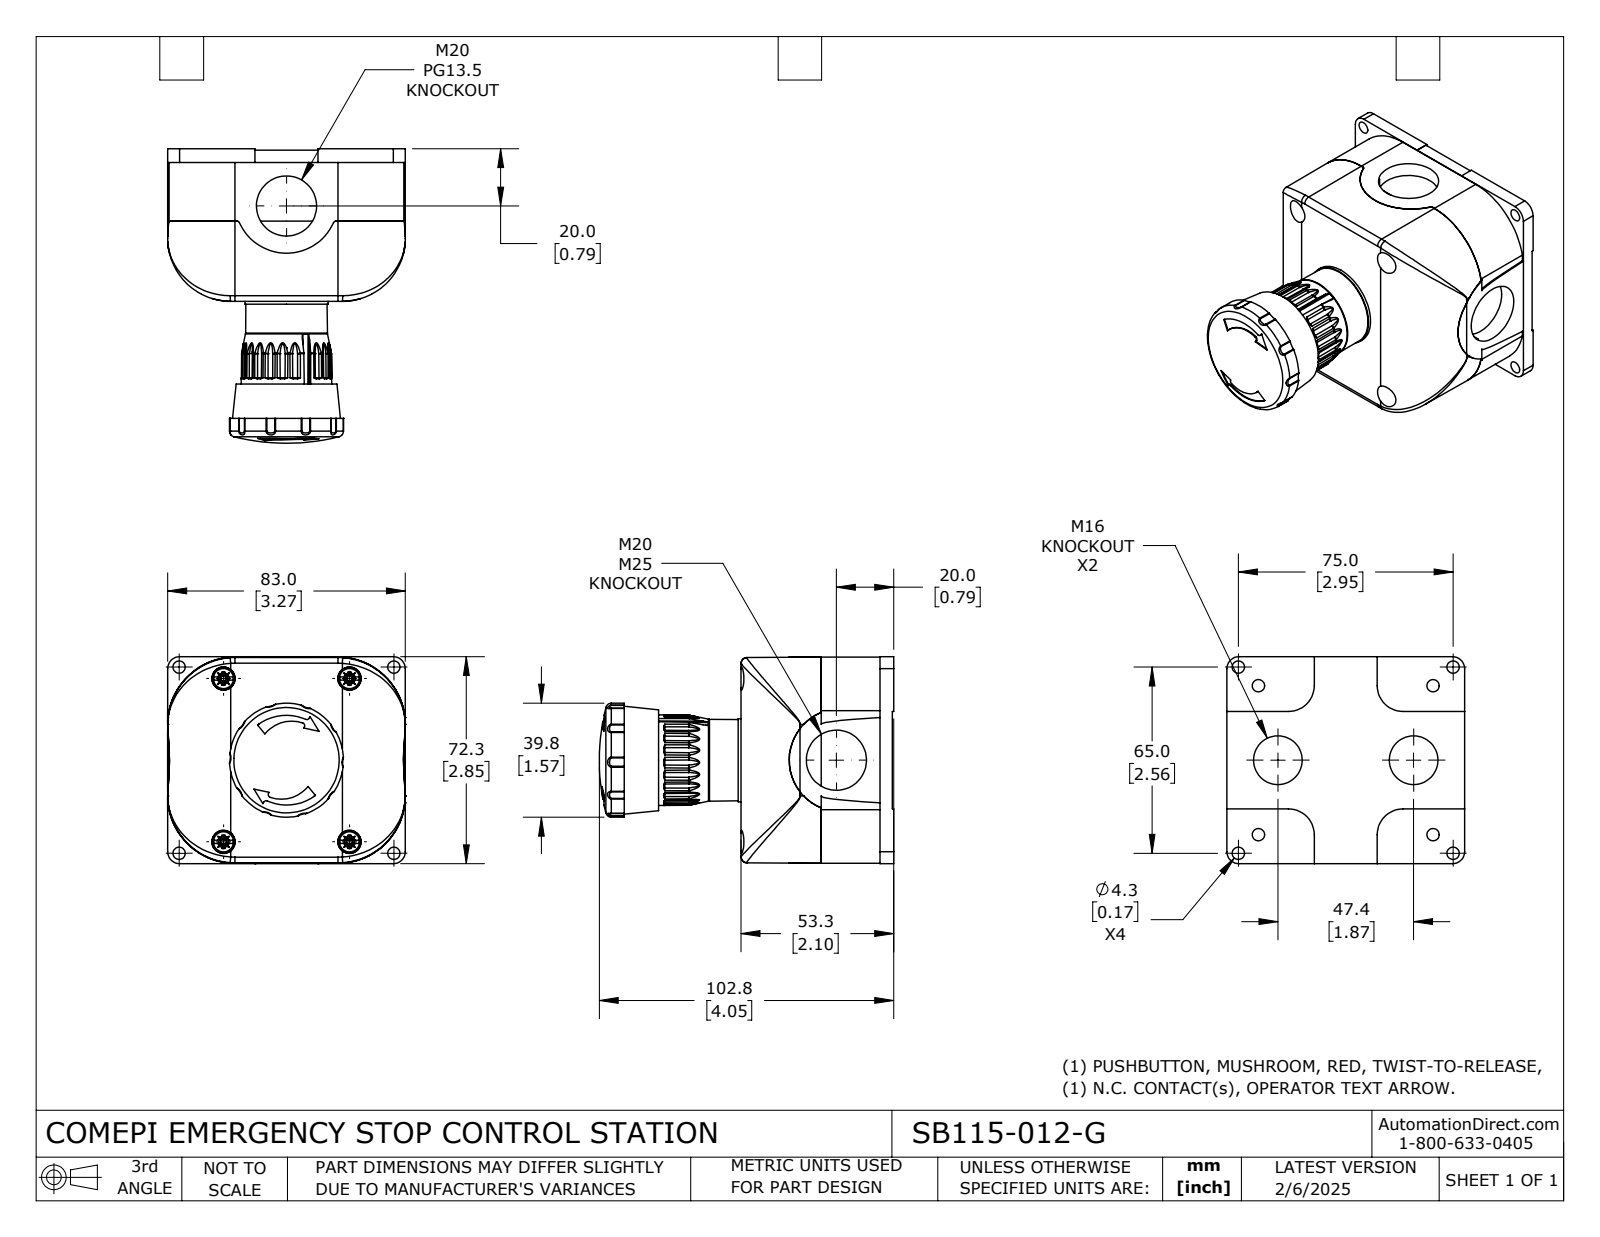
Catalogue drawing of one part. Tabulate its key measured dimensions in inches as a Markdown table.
| quantity | value |
| --- | --- |
| part name | SB115-012-G |
| STEP written by | SolidWorks 2024 (CONFIG_CONTROL_DESIGN) |
| units | inches |
| bodies | 5 solids, 901 faces (353 planar, 192 cylindrical, 356 other) |
| overall size | 4.048 × 3.268 × 2.846 |
| volume | 14.31 in³ |
| surface area | 106.3 in² |
| round holes (diameter × count) | 0.169 × 8, 0.323 × 4, 0.669 × 2, 0.827 × 2, 0.051 × 1, 0.713 × 1, 0.854 × 1 |
| round bosses / shafts (diameter × count) | 0.276 × 4, 1.142 × 1, 0.925 × 1, 0.874 × 1, 0.843 × 1 |
| partial cylindrical surfaces (radius × count) | 0.039 × 28, 0.268 × 10, 0.035 × 4, 0.079 × 4, 0.354 × 4, 0.38 × 4, 0.925 × 4, 0.01 × 2 |
| main face-to-face distances | 0.976, 0.098, 0.878, 2.079, 1.98, 1.102, 0.118, 0.02, 0.996, 2.098 |
| hole center spacings | 0.376, 1.058, 1.39, 1.578, 1.954, 2.32, 2.367, 2.689 |
